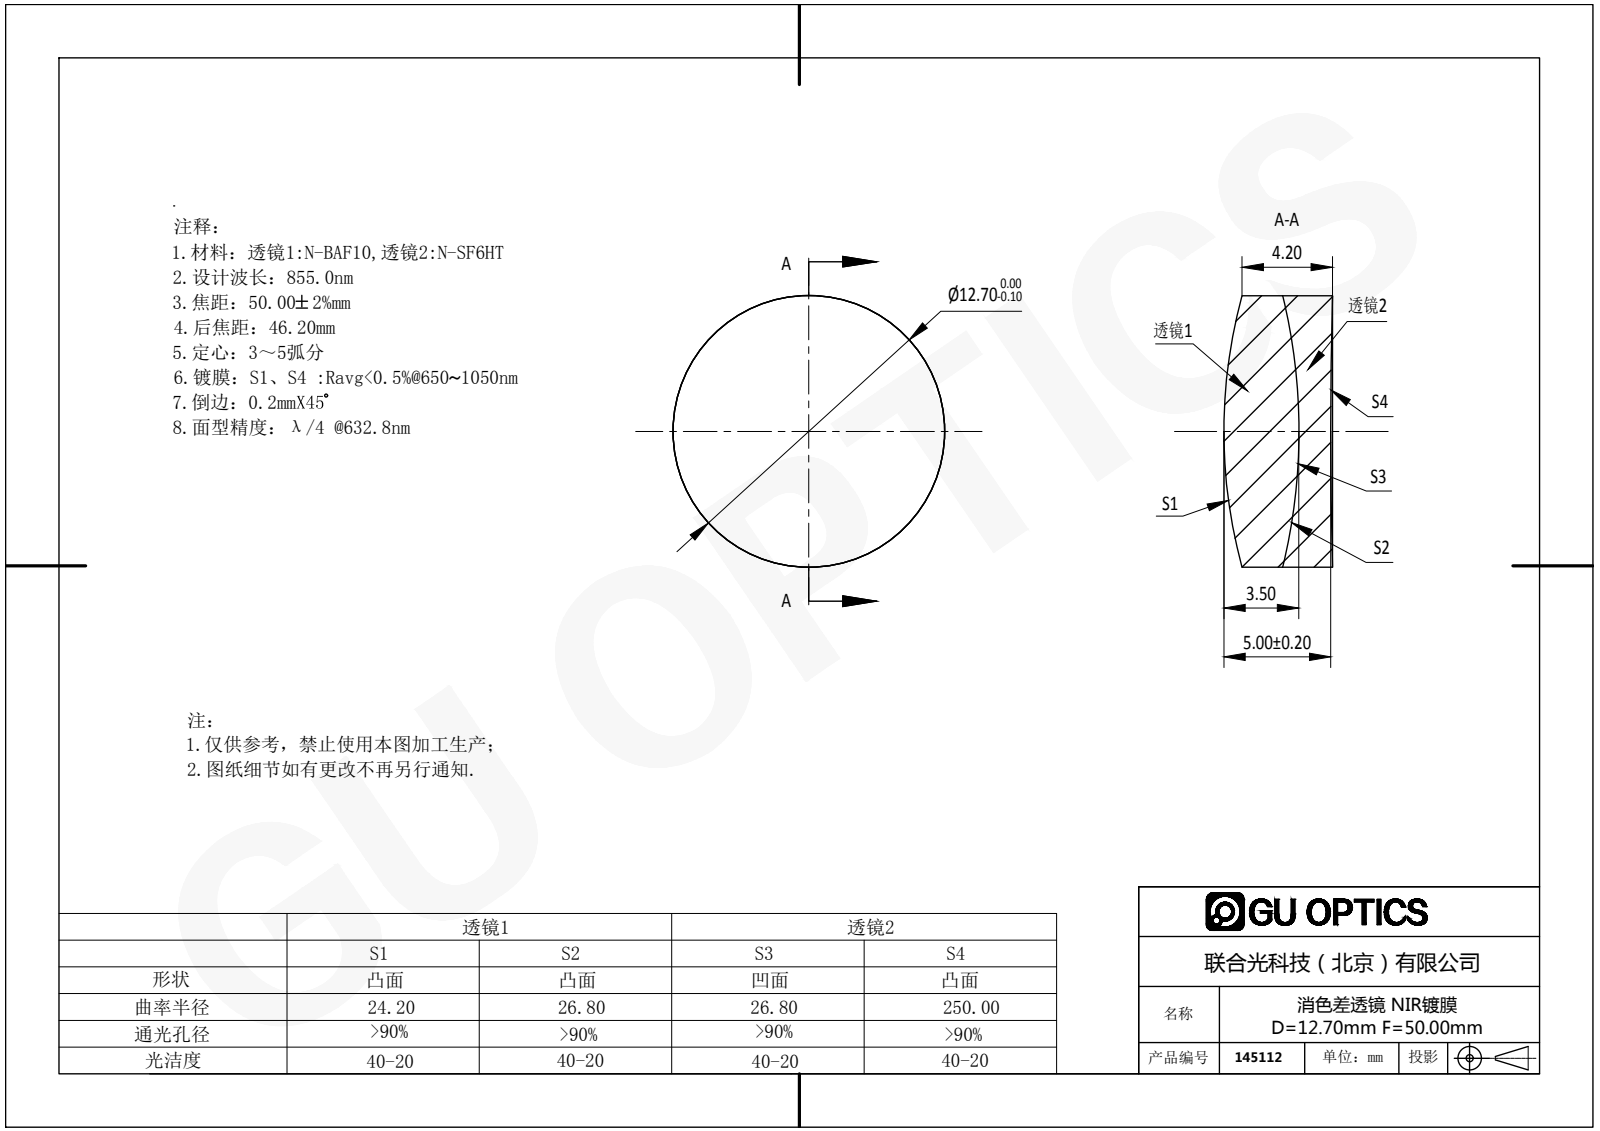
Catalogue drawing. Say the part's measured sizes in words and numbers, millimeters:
The part is named "145112". Its 3-D file was written by "SolidWorks 2016 (AUTOMOTIVE_DESIGN)". It is 2 solids with 12 faces: 0 planar, 4 cylindrical and 8 other. Overall it measures 12.7 by 12.7 by 5.08 millimeters. Its volume is 585 cubic millimeters and its surface area 682 square millimeters. Round bosses or shafts: 1 of diameter 12.7.
